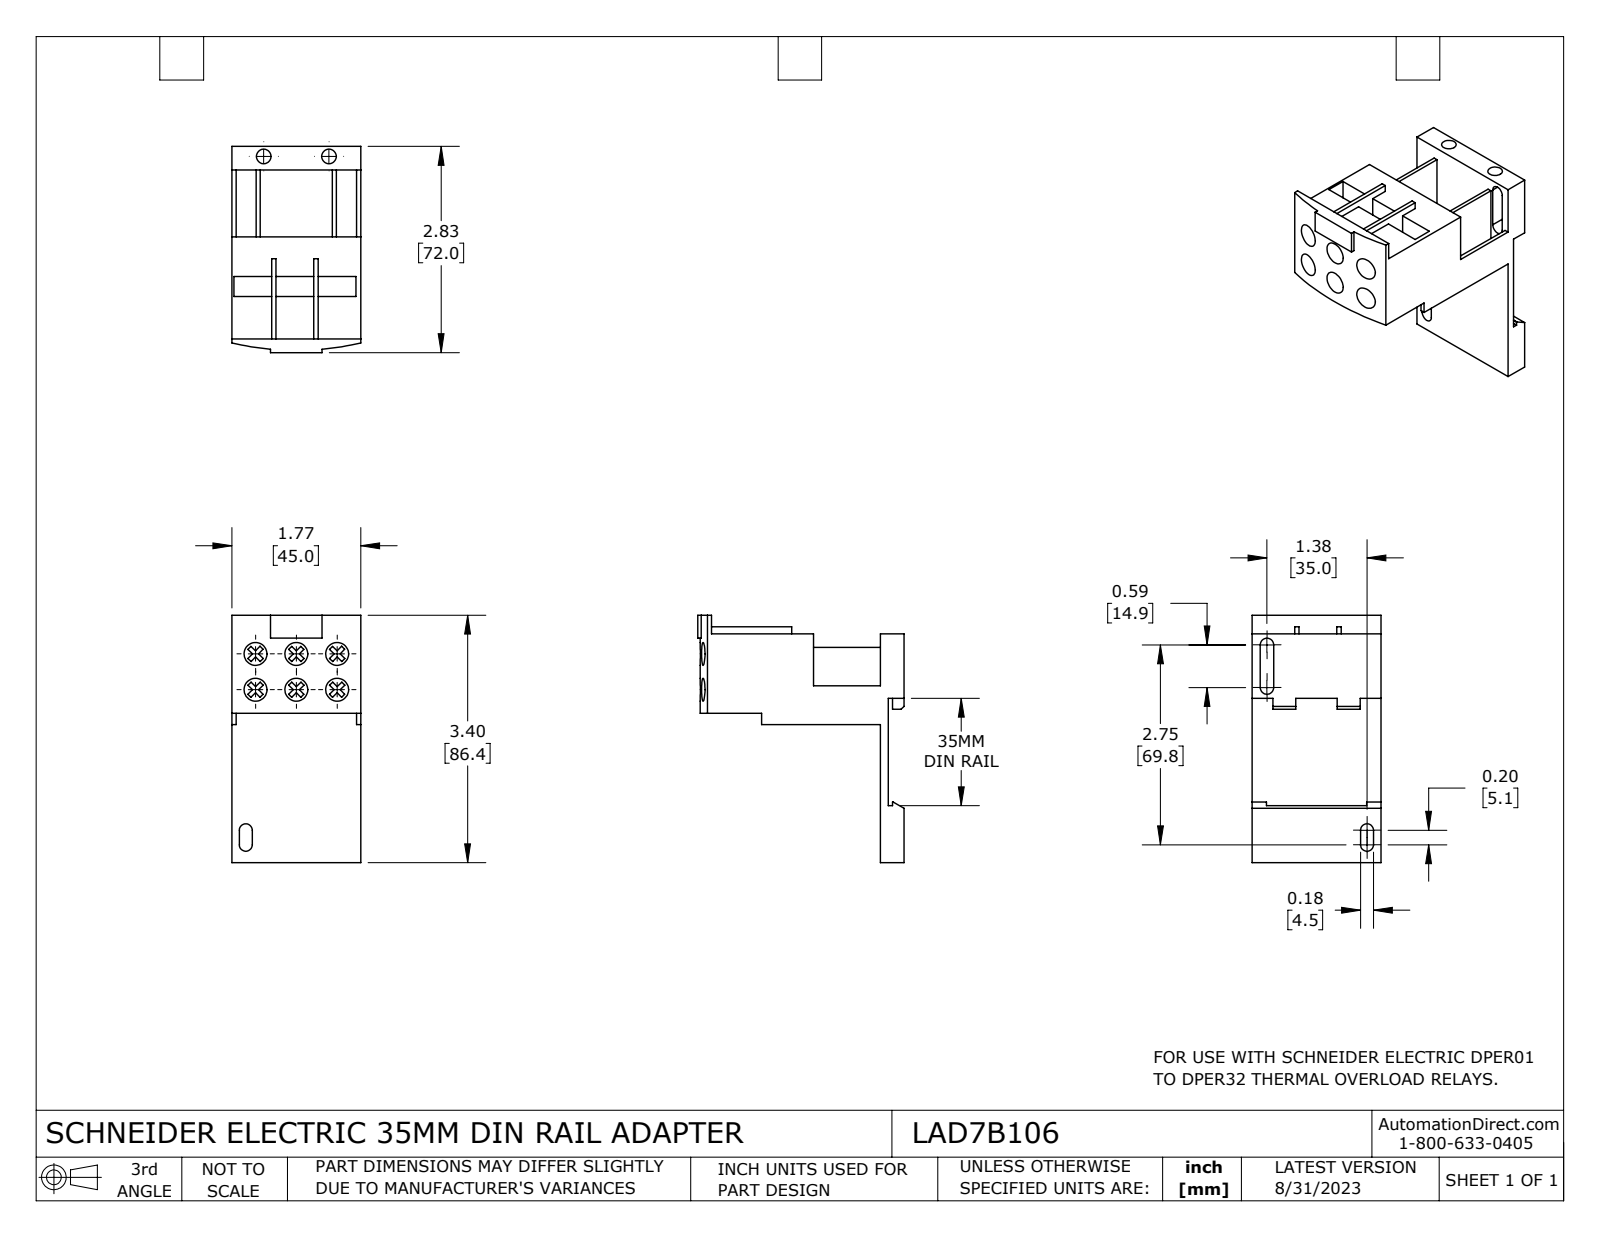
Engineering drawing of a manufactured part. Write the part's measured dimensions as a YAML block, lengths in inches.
part_name: "LAD7B106"
step_written_by: "SolidWorks 2021 (CONFIG_CONTROL_DESIGN)"
units: inches
bodies: {solids: 1, faces: 189, planar: 166, cylindrical: 23, other: 0}
overall_size: [3.402, 2.835, 1.772]
volume: 4.046
surface_area: 42.58
round_holes:
  - {diameter: 0.315, count: 6}
  - {diameter: 0.201, count: 2}
partial_cylinders:
  - {radius: 0.089, count: 2}
  - {radius: 0.093, count: 2}
  - {radius: 3.884, count: 1}
face_to_face_distances: [0.323, 0.106, 0.217, 1.772, 1.091, 0.992, 0.276, 0.059, 1.047, 0.921]
hole_center_spacings: [0.561, 0.746, 0.492, 1.122, 1.225, 0.898]
